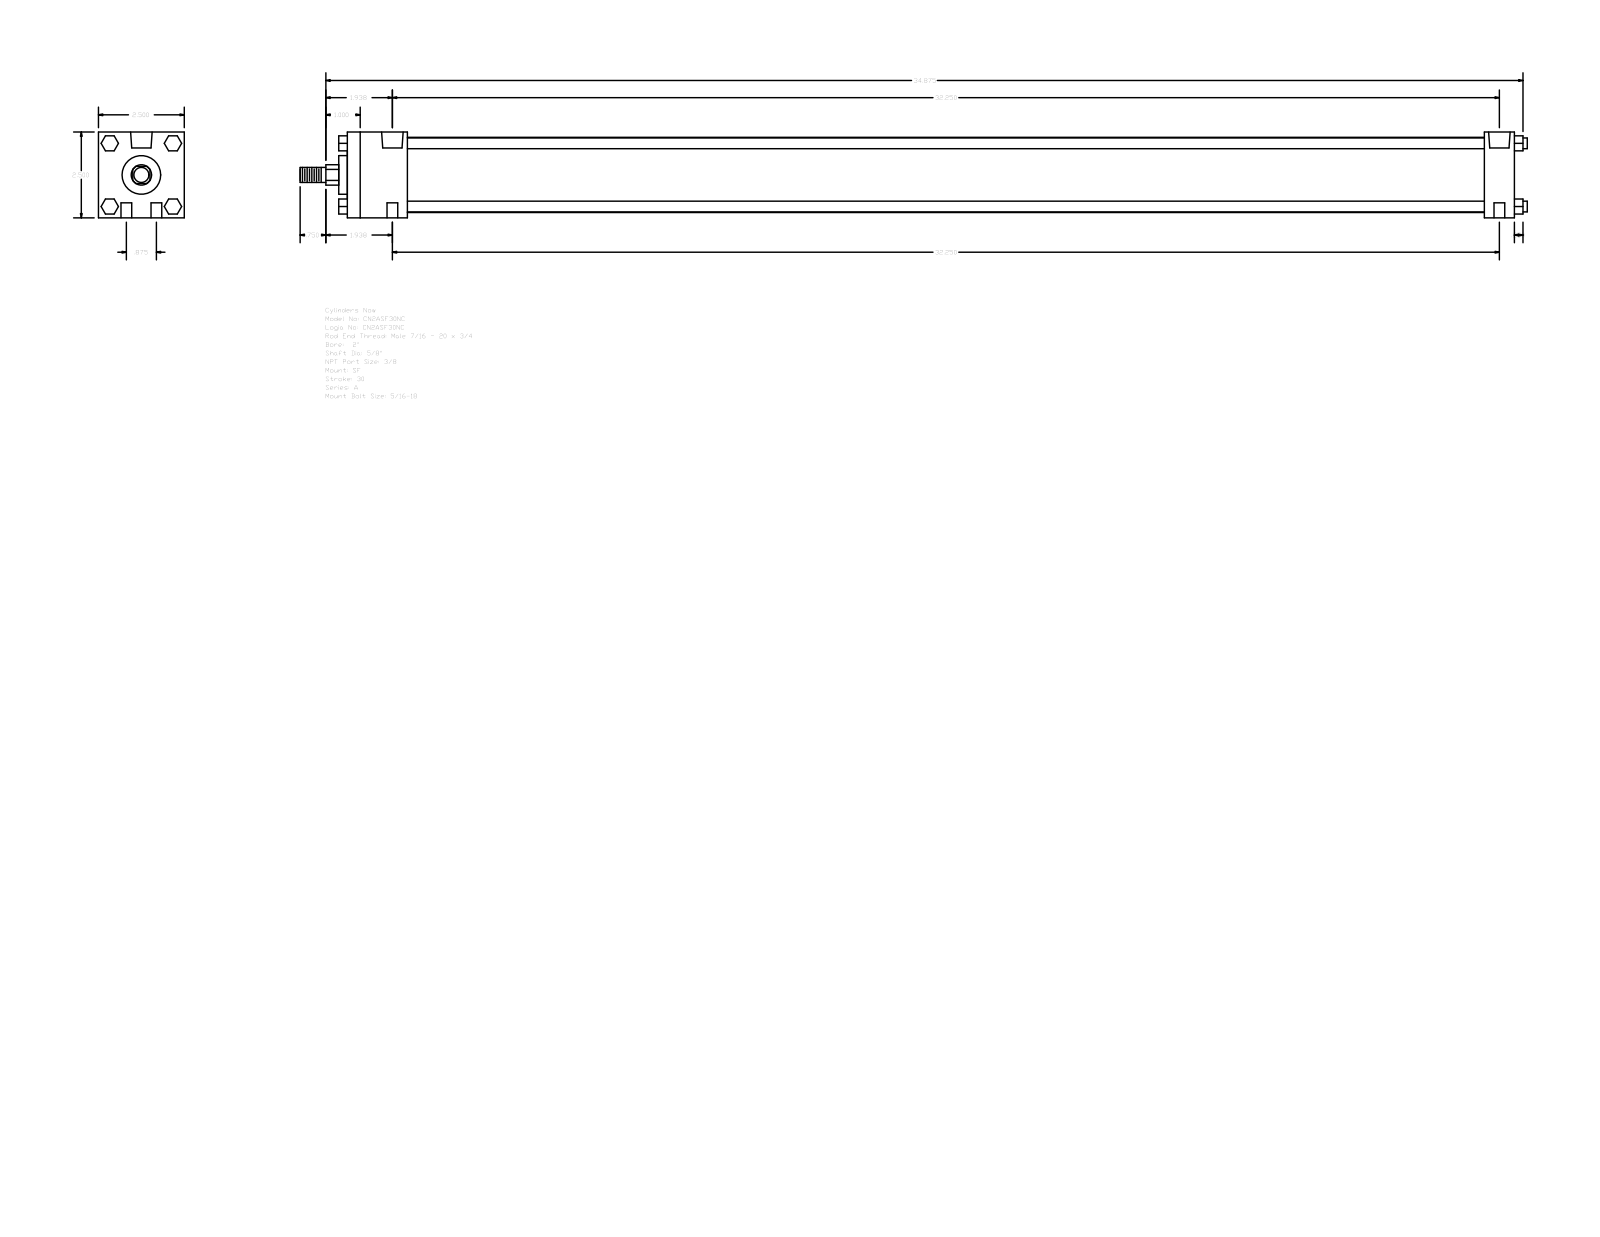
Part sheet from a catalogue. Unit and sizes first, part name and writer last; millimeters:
Units: millimetres
Overall size (bounding box): 908.05 × 63.5 × 63.5
Round holes (diameter × count): ⌀7.94 ×4, ⌀5.56 ×2, ⌀15.93 ×2
Round bosses / shafts (diameter × count): ⌀7.94 ×4, ⌀55.63 ×1, ⌀28.57 ×1, ⌀15.88 ×1, ⌀11.11 ×1
Partial cylindrical surfaces — rounded edges, fillets, slot ends (radius × count): R7.54 ×1
Main face-to-face distances: 63.5, 863.6, 841.37, 22.23, 44.45, 796.92, 819.15, 6.35, 869.95, 50.8
Hole centre spacings: 11.11, 819.23, 819.15, 22.22, 819.45, 811.2
Bodies: 0 solids, 124 faces (94 planar, 30 cylindrical, 0 other)
Part name (STEP PRODUCT): A_SF__0200_0.625
STEP written by: GSSL Pune (CONFIG_CONTROL_DESIGN)
